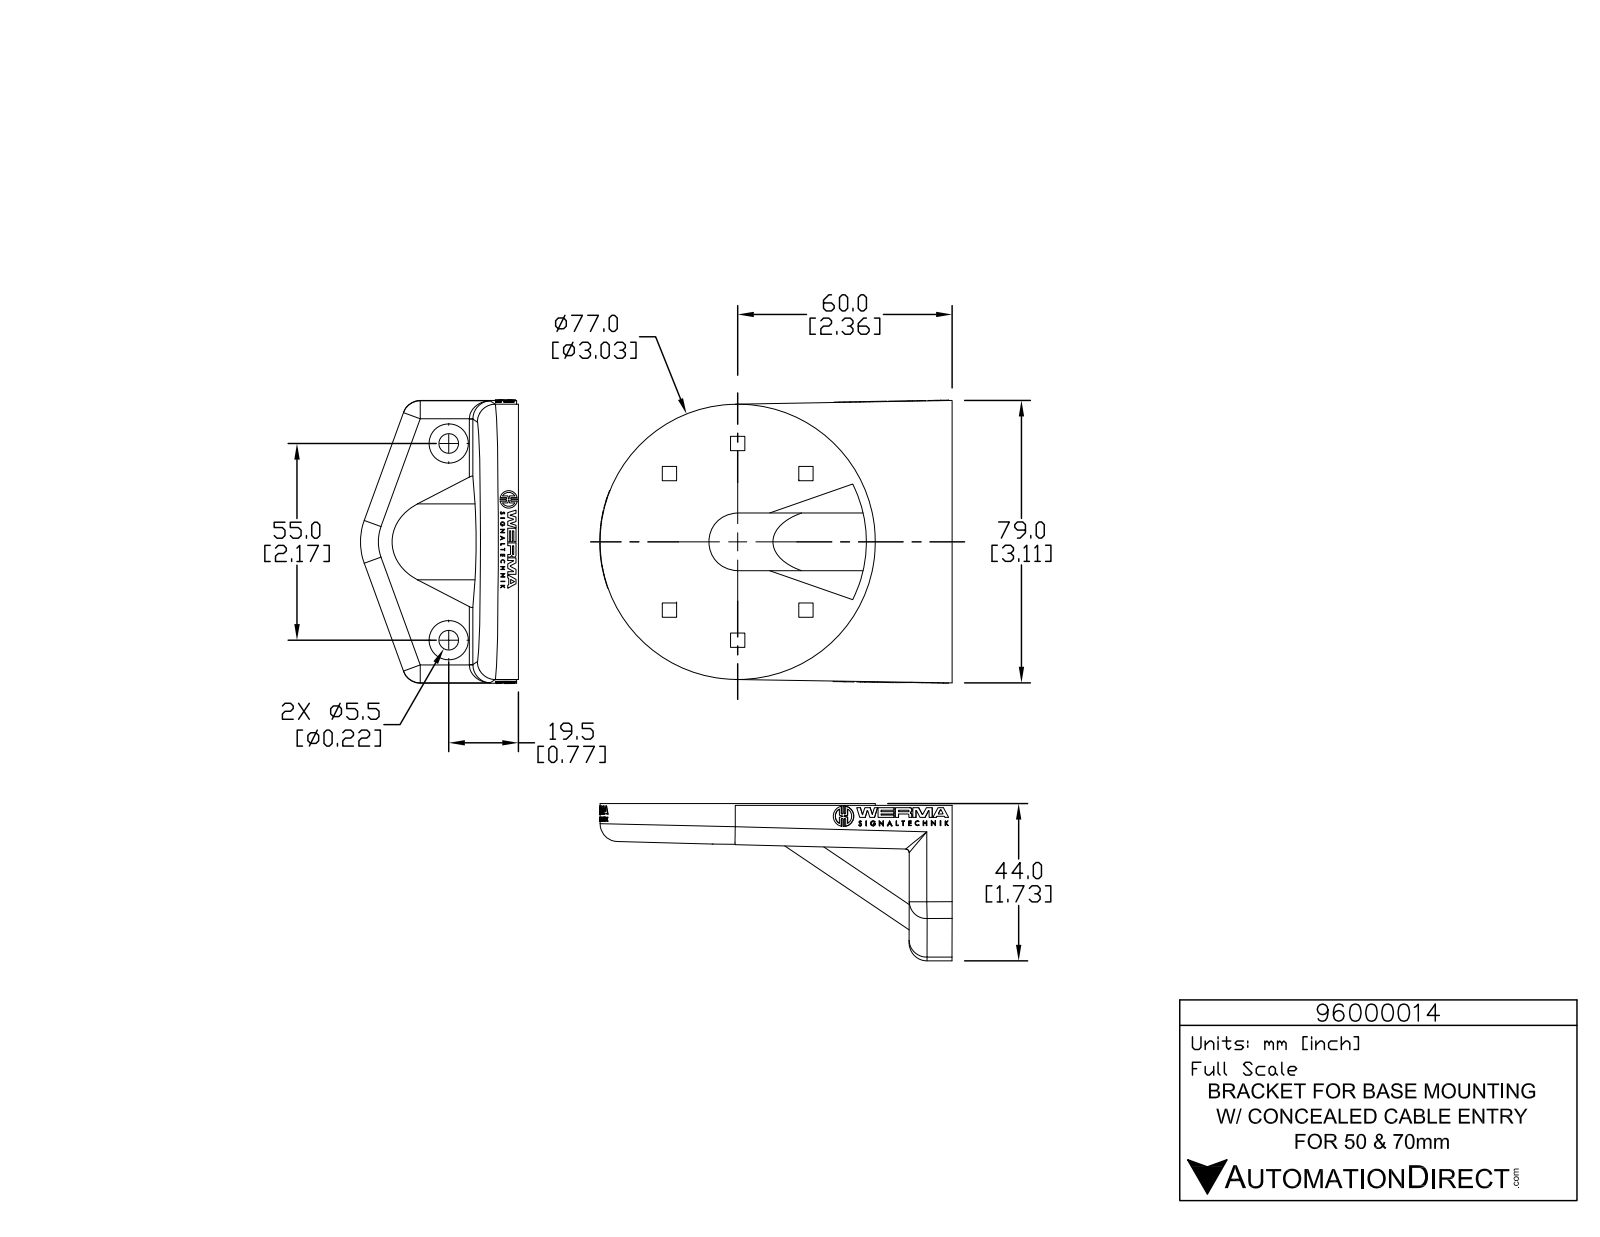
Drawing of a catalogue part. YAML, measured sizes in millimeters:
part_name: "96000014"
step_written_by: "SolidWorks 2015 (AUTOMOTIVE_DESIGN)"
units: millimeters
bodies: {solids: 1, faces: 838, planar: 616, cylindrical: 214, other: 8}
overall_size: [98.6, 79.3, 44.2]
volume: 84440
surface_area: 25600
round_holes:
  - {diameter: 1, count: 2}
  - {diameter: 5.5, count: 2}
  - {diameter: 11, count: 2}
  - {diameter: 0.8, count: 1}
round_bosses_or_shafts:
  - {diameter: 5.7, count: 2}
  - {diameter: 1.4, count: 2}
  - {diameter: 77, count: 1}
  - {diameter: 4.9, count: 1}
  - {diameter: 1.2, count: 1}
partial_cylinders:
  - {radius: 5, count: 8}
  - {radius: 0.2, count: 4}
  - {radius: 0.2, count: 4}
  - {radius: 0.2, count: 4}
  - {radius: 3.3, count: 4}
  - {radius: 0.1, count: 2}
  - {radius: 0.1, count: 2}
  - {radius: 0.2, count: 2}
face_to_face_distances: [0.5, 3, 3.5, 12, 4, 5.5, 6, 2.5, 19.1, 38.2]
hole_center_spacings: [27.1, 35.8, 55]
